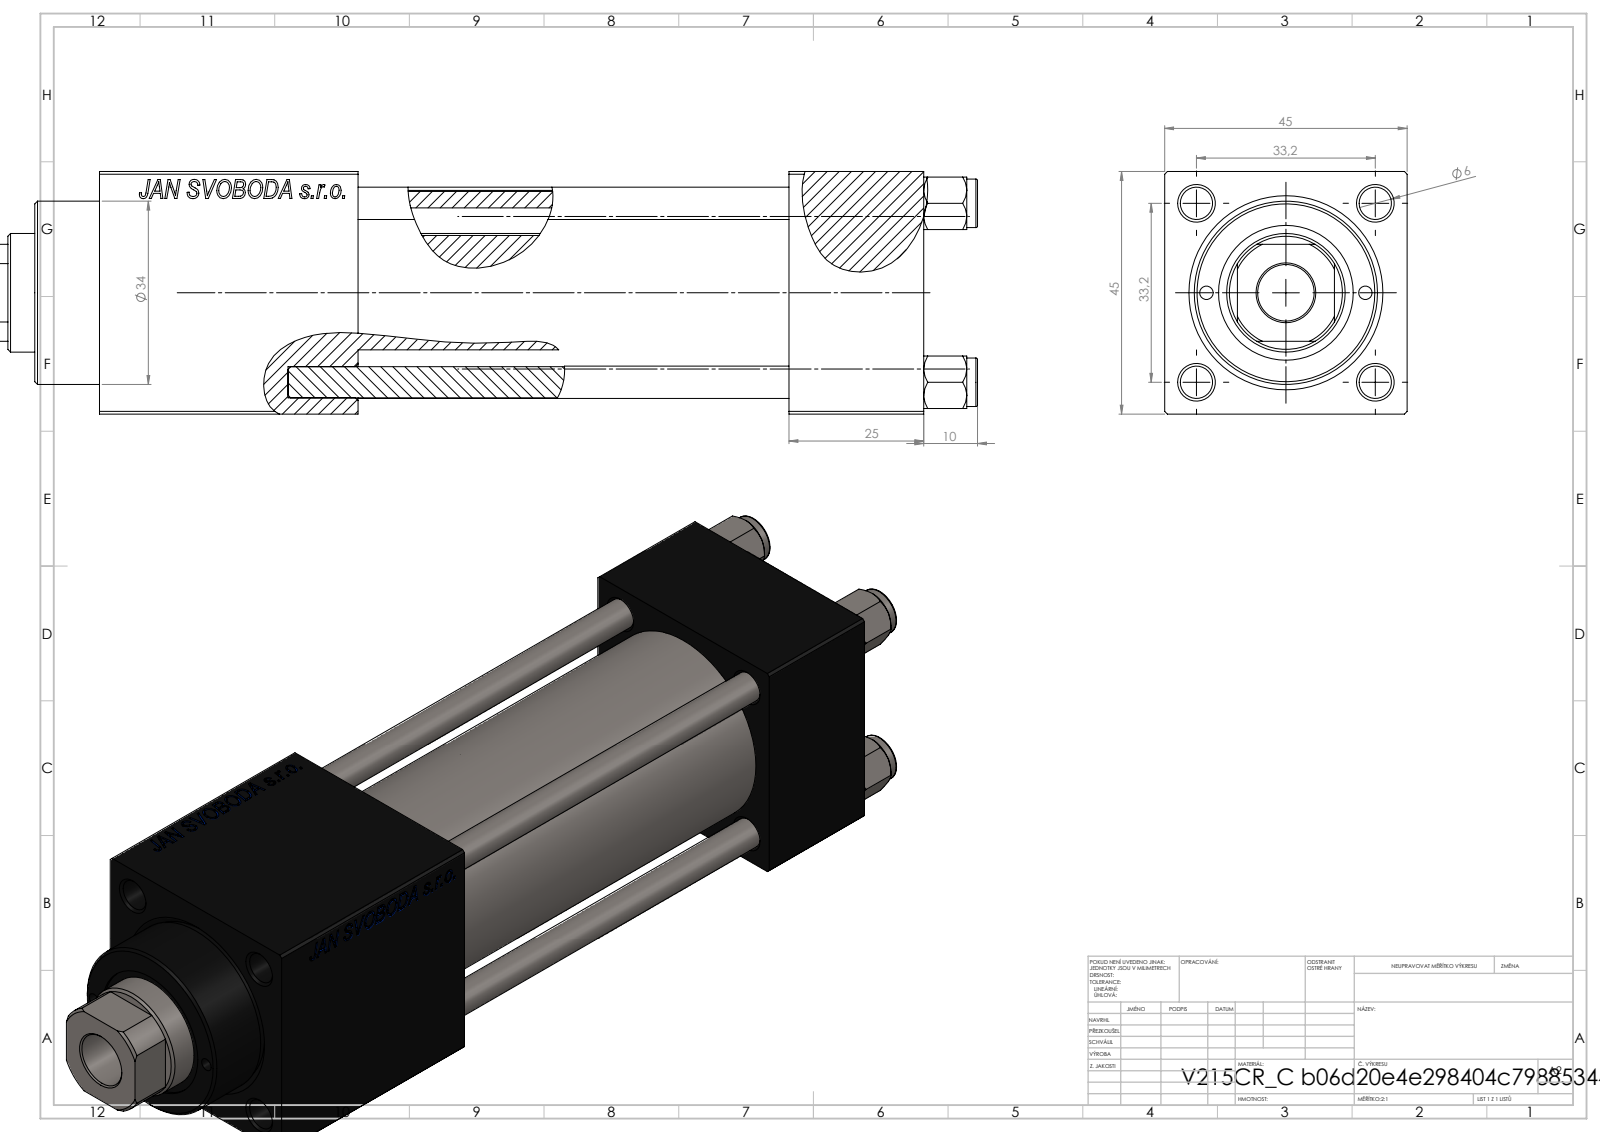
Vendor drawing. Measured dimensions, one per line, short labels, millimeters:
name: NUT_M5_C; V215CR_C_Body; V215CR_C_TYCINKA; V215_VC_A (+1 more)
written by: SolidWorks 2019 (CONFIG_CONTROL_DESIGN)
unit: mm
bodies: 11 solids, 1153 faces (527 planar, 90 cylindrical, 536 other)
size: 188 × 45 × 45
volume: 234 385 mm³; area: 82 502 mm²
holes: 4× ⌀6, 2× ⌀2.5, 2× ⌀7, 2× ⌀13.16, 2× ⌀20, 1× ⌀10.5, 1× ⌀22, 1× ⌀24, 1× ⌀25, 1× ⌀32, 1× ⌀33
bosses: 4× ⌀9, 1× ⌀38, 1× ⌀34
rounds: 1× R10.5
face distances: 45, 25, 153, 105, 80, 128, 48, 124.3, 99.3, 19.3
hole spacings: 16.7, 23.48, 33.2, 35.47, 14.75, 46.95, 29.5, 105.5
